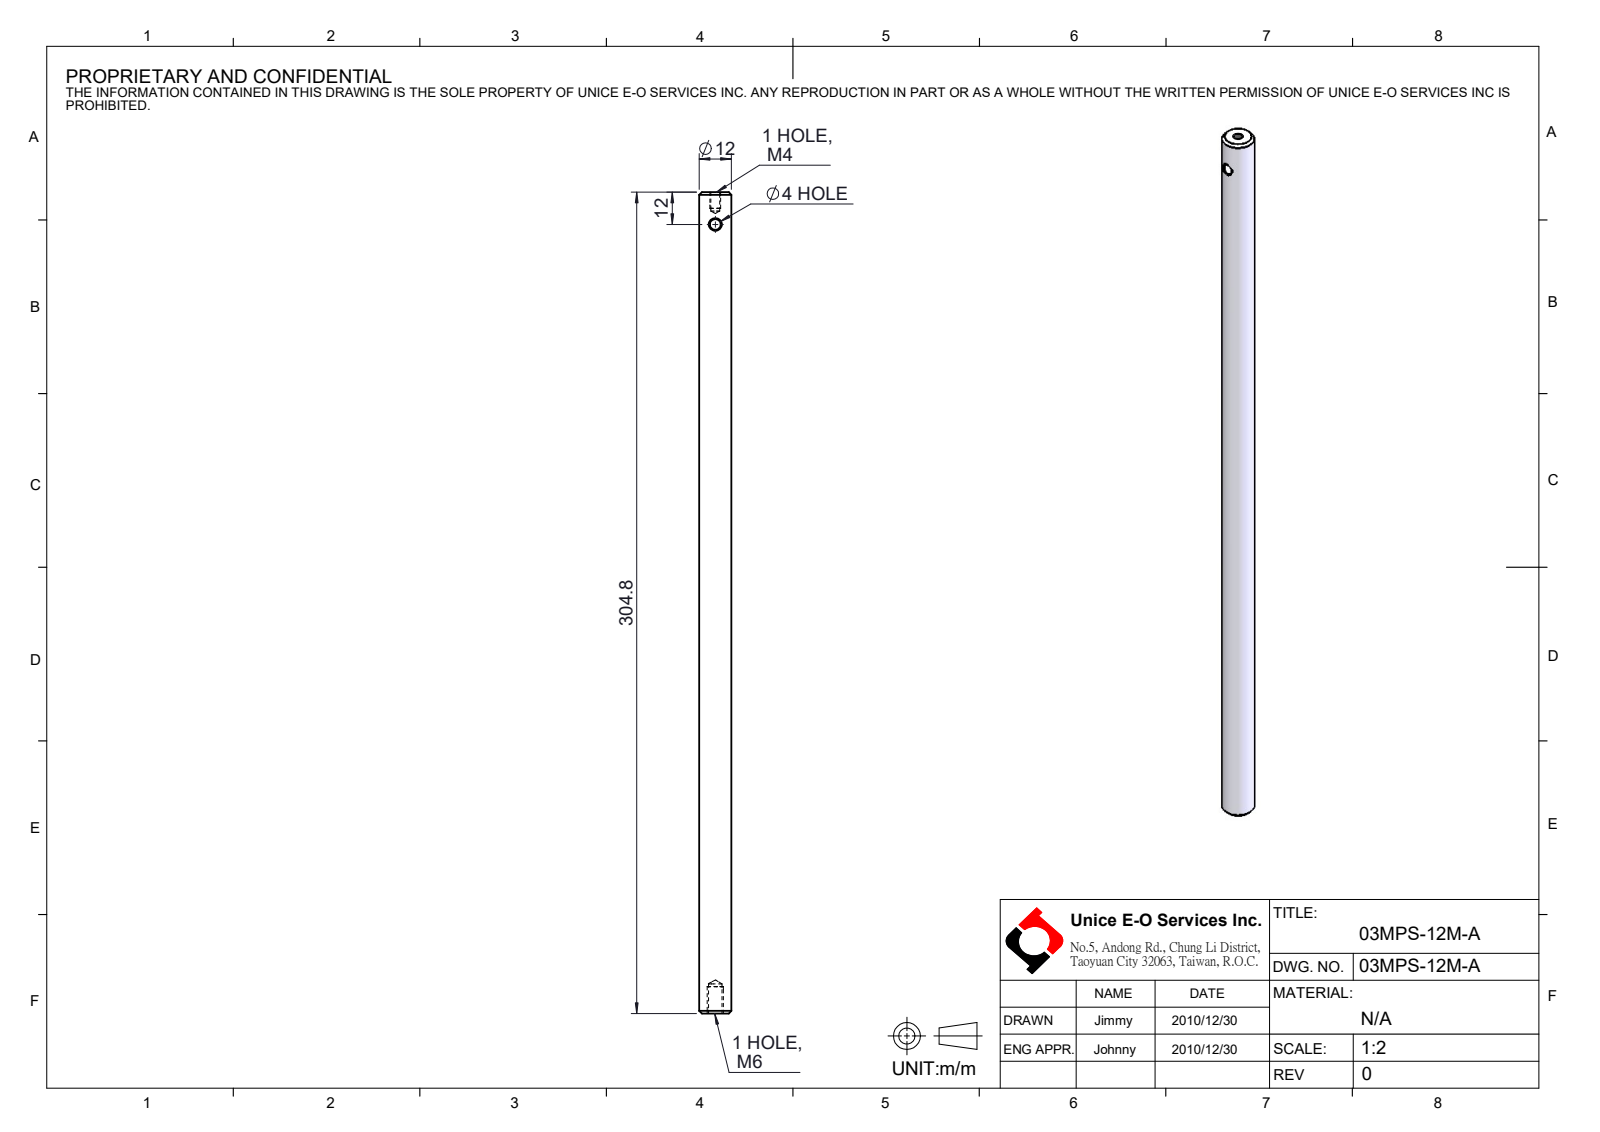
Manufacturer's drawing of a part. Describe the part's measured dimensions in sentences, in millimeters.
The part is named "03MPS-12M-A". Its 3-D file was written by "SolidWorks 2016 (CONFIG_CONTROL_DESIGN)". It is 1 solid with 22 faces: 2 planar, 8 cylindrical and 12 other. Overall it measures 304.8 by 12 by 12 millimeters. Its volume is 33 998 cubic millimeters and its surface area 12 034 square millimeters. Round holes: 1 of diameter 3.3, 1 of diameter 4, 1 of diameter 5. Round bosses or shafts: 1 of diameter 12. The main face-to-face distances are 304.8.
